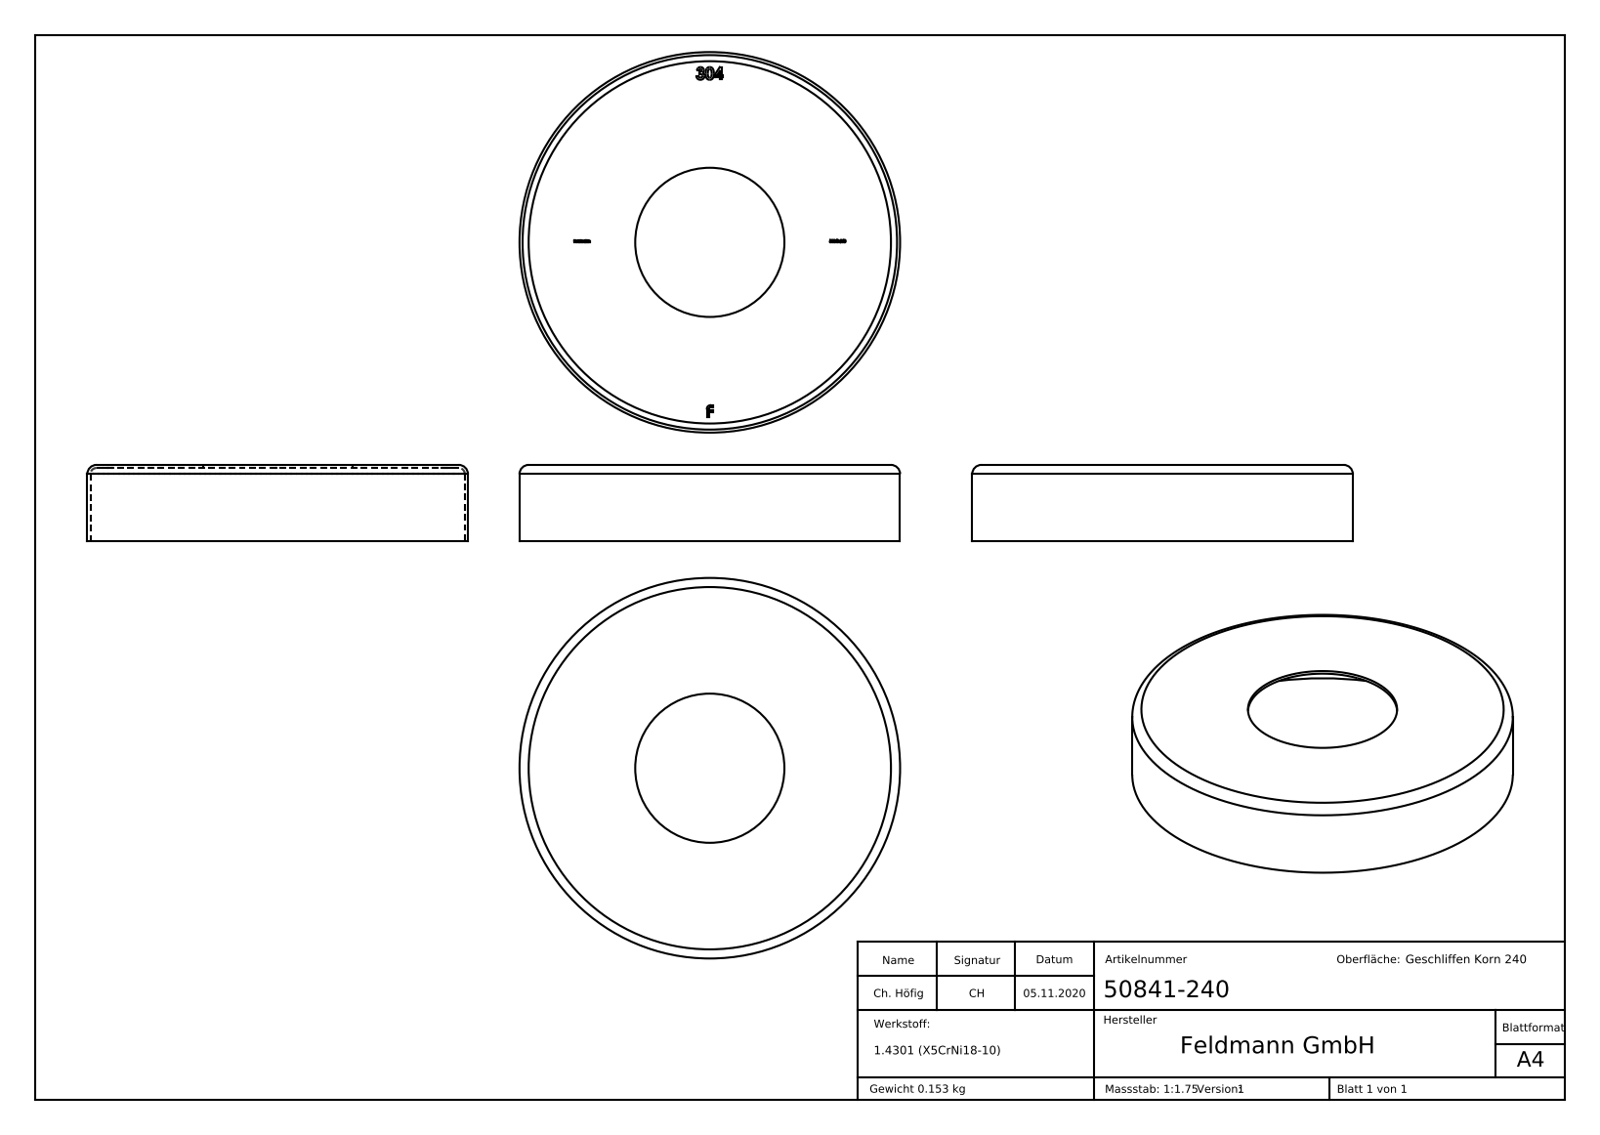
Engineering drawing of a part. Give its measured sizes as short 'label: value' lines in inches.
name: 50841-240
written by: SolidWorks 2018 (CONFIG_CONTROL_DESIGN)
unit: in
bodies: 1 solid, 296 faces (164 planar, 6 cylindrical, 126 other)
size: 4.921 × 4.921 × 0.984
volume: 1.178 in³; area: 60.74 in²
holes: 1× ⌀1.929, 1× ⌀4.843
bosses: 1× ⌀4.921
face distances: 0.039, 0.945, 0.984, 0.949, 0.035, 0.028, 0.197, 0.169, 1.669, 0.023
